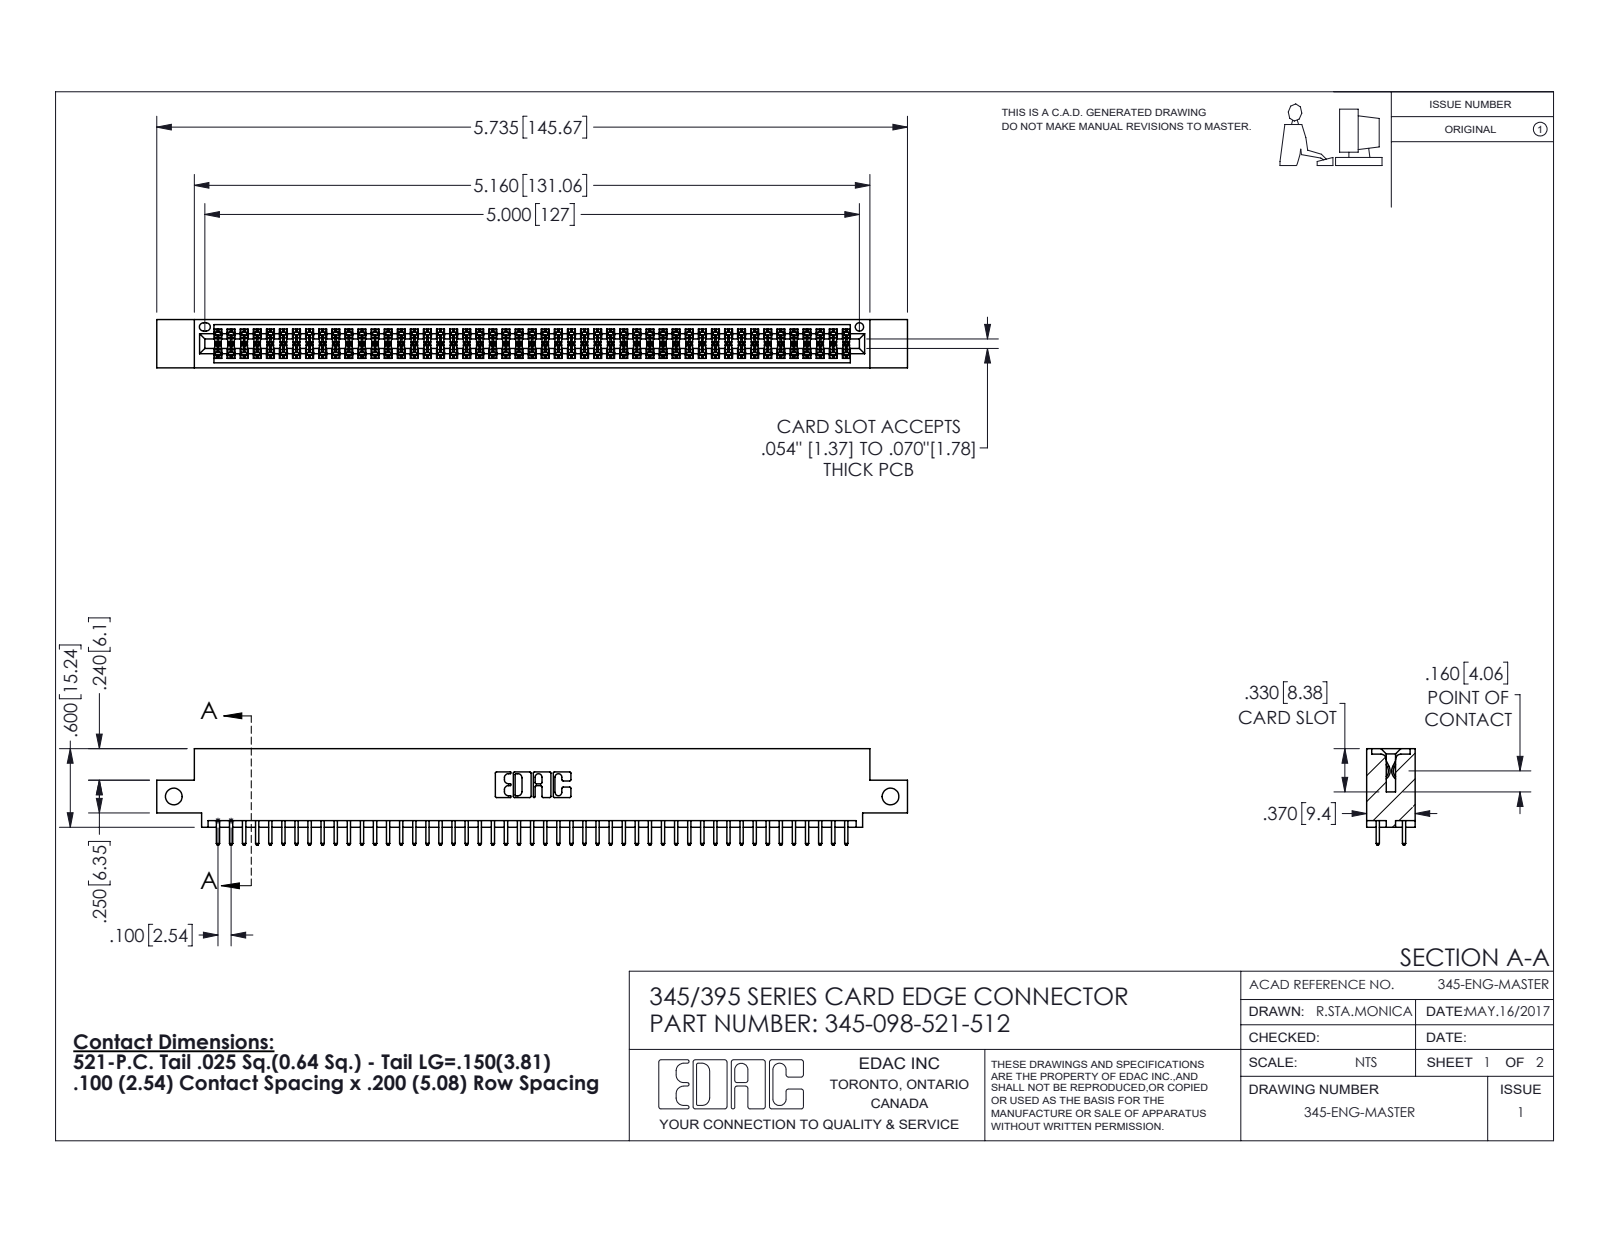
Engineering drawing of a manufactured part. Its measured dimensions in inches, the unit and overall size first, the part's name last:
Units: inches
Overall size (bounding box): 5.735 × 0.737 × 0.37
Round holes (diameter × count): ⌀0.128 ×2, ⌀0.064 ×1
Partial cylindrical surfaces — rounded edges, fillets, slot ends (radius × count): R0.006 ×147, R0.01 ×98, R0.01 ×22, R0.007 ×6, R0.031 ×6, R0.026 ×3, R0.014 ×2, R0.019 ×2
Main face-to-face distances: 0.298, 0.072, 0.2, 0.098, 0.272, 0.025, 0.37, 0.225, 0.175, 0.149
Hole centre spacings: 5.475
Volume: 0.855 in³ · Surface area: 31.85 in²
Bodies: 99 solids, 5030 faces (3318 planar, 1712 cylindrical, 0 other)
Part name (STEP PRODUCT): 345-292-001_345-293-121; 345 Part_0.110 Offset - Side Mount; 345-098-521-512
STEP written by: SolidWorks 2016 (CONFIG_CONTROL_DESIGN)
